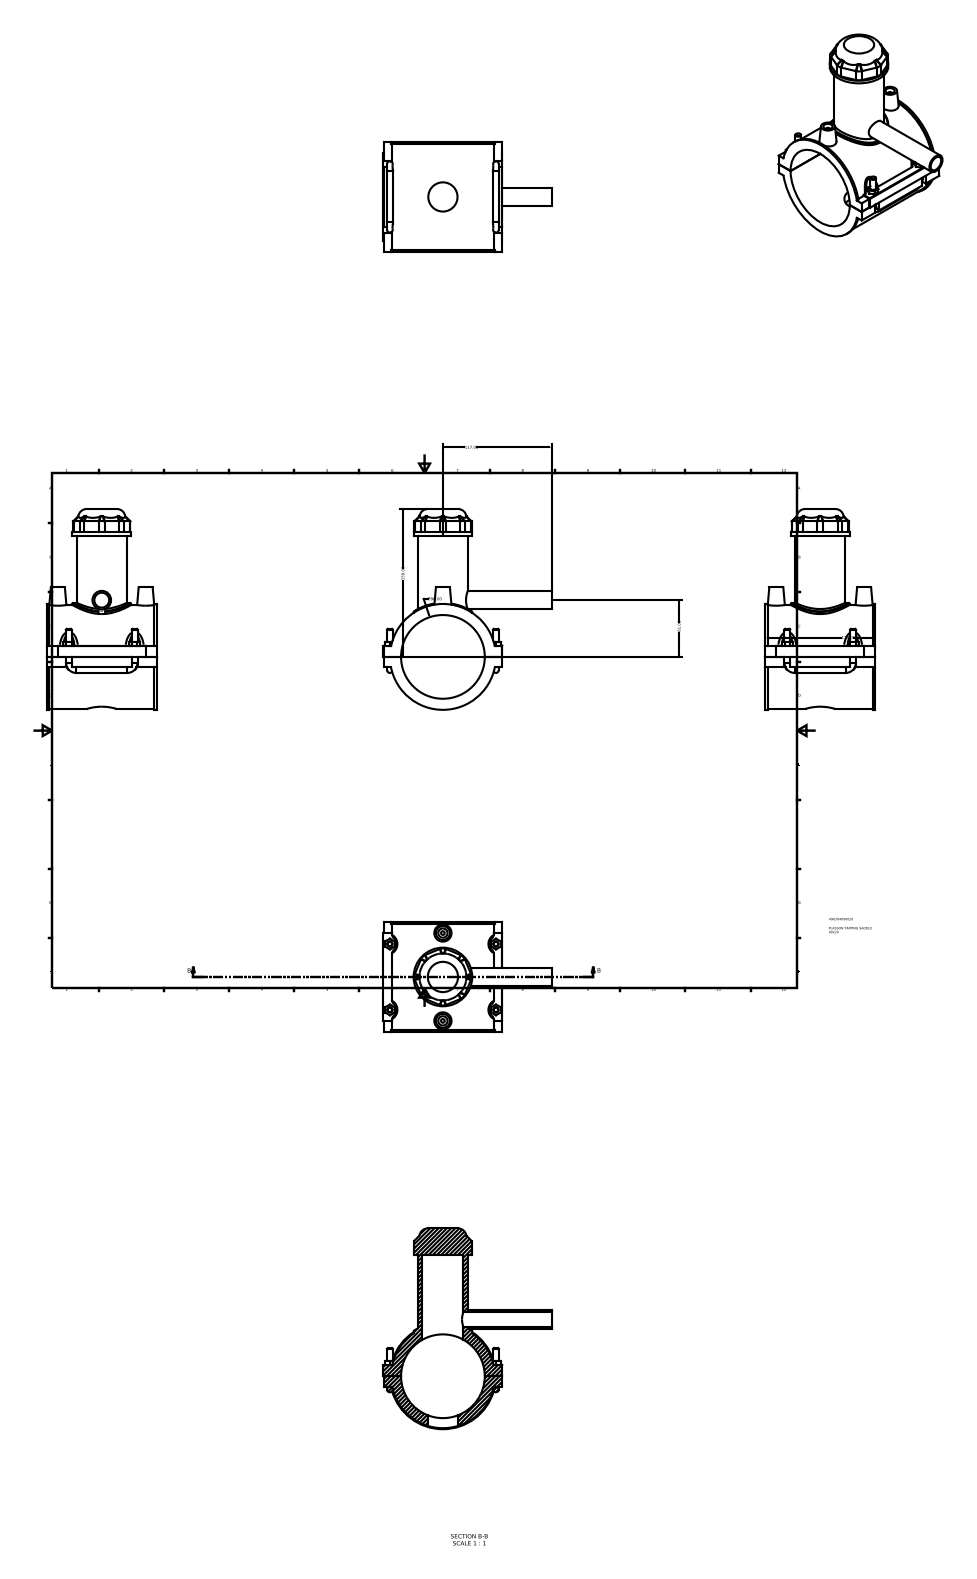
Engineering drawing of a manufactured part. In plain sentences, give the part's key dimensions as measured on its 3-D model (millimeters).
The part is named "496304090020". Its 3-D file was written by "Autodesk Inventor 2015 (AUTOMOTIVE_DESIGN)". It is 1 solid with 224 faces: 125 planar, 55 cylindrical and 44 other. Overall it measures 215.92 by 181 by 118 millimeters. Its volume is 571 504 cubic millimeters and its surface area 144 970 square millimeters. Round holes: 2 of diameter 10, 1 of diameter 16, 1 of diameter 31.36, 1 of diameter 44.1, 1 of diameter 90. Round bosses or shafts: 6 of diameter 6, 2 of diameter 4, 1 of diameter 113.83, 1 of diameter 111.6, 1 of diameter 63, 1 of diameter 53.55, 1 of diameter 20. Partial cylindrical surfaces (rounded edges, fillets, slot ends): 8 of radius 9, 4 of radius 3, 4 of radius 7.5, 1 of radius 0.5, 1 of radius 58.03. The main face-to-face distances are 118, 1, 130.55, 130.45, 127, 11.2, 11.3, 141.75, 23.5, 12.3. The hole center spacings are 47.2, 94.4.
